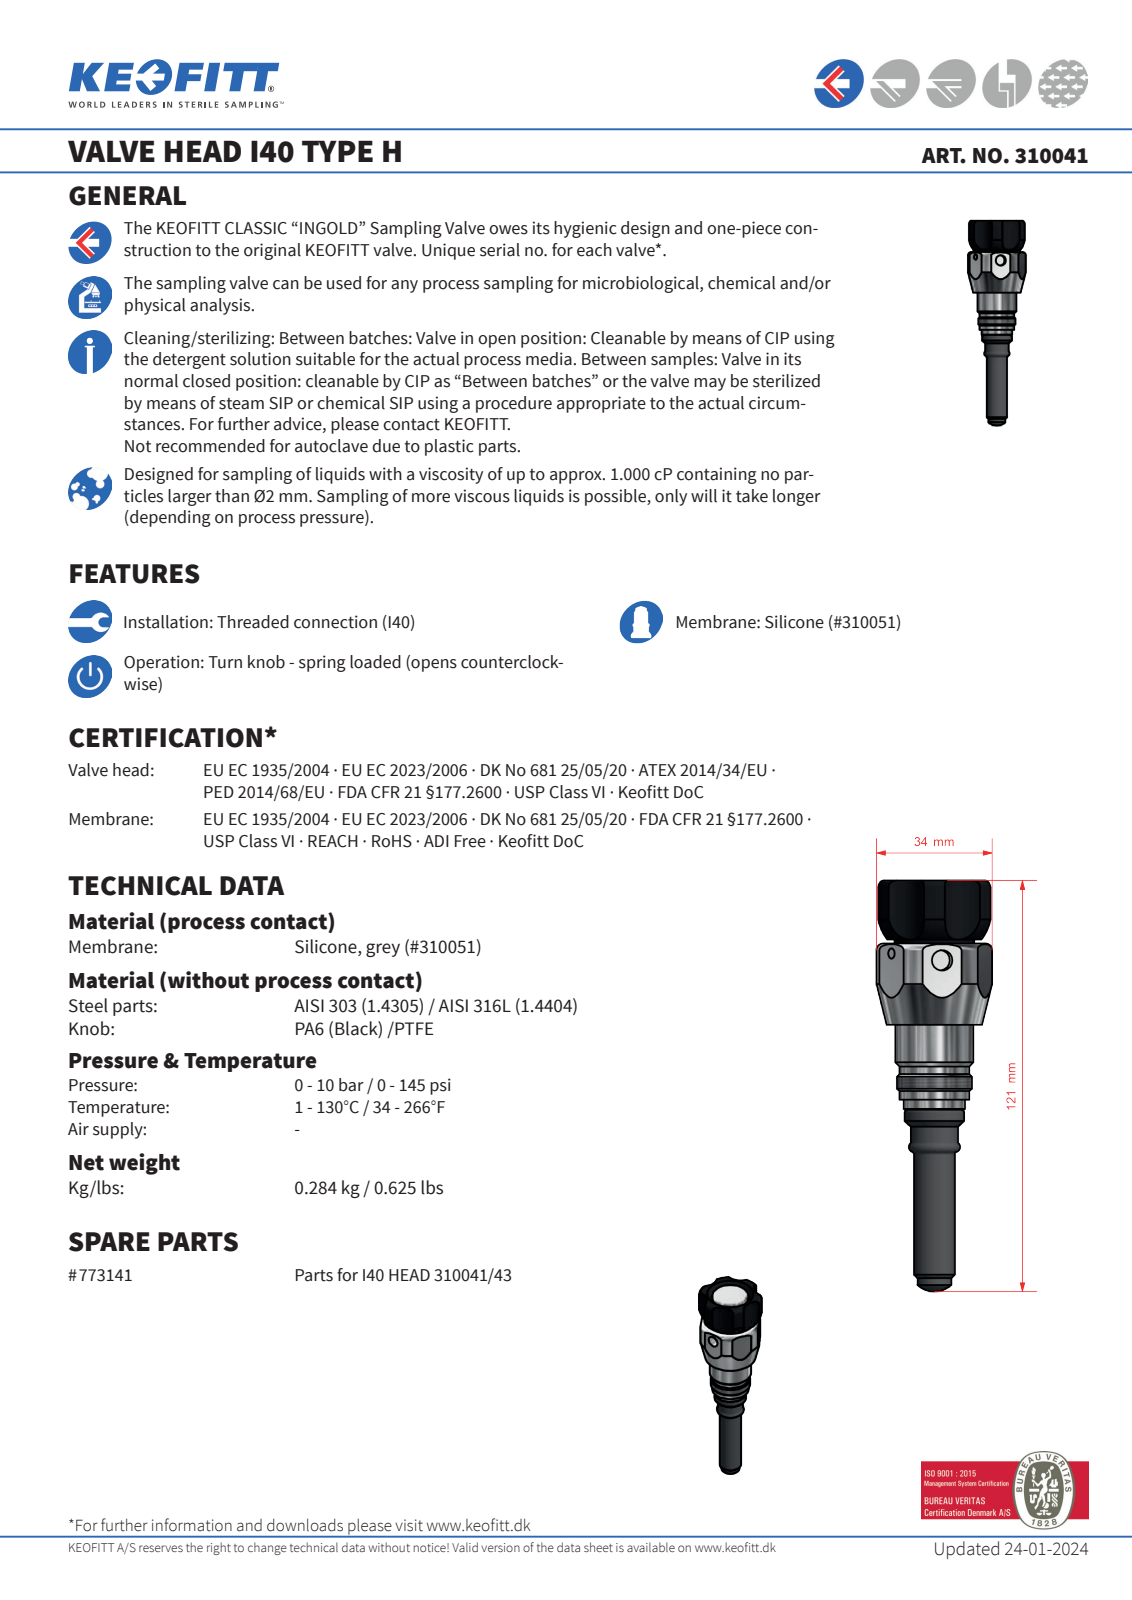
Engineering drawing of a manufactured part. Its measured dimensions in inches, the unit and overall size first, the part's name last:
Units: inches
Overall size (bounding box): 4.764 × 1.378 × 1.339
Round holes (diameter × count): ⌀0.238 ×2, ⌀0.12 ×1, ⌀0.402 ×1, ⌀0.583 ×1, ⌀0.669 ×1, ⌀0.713 ×1, ⌀0.732 ×1, ⌀0.762 ×1, ⌀0.811 ×1
Round bosses / shafts (diameter × count): ⌀0.925 ×1, ⌀0.906 ×1, ⌀0.866 ×1, ⌀0.807 ×1, ⌀0.787 ×1, ⌀0.709 ×1, ⌀0.689 ×1, ⌀0.61 ×1
Partial cylindrical surfaces — rounded edges, fillets, slot ends (radius × count): R0.315 ×6, R0.669 ×1, R0.689 ×1
Main face-to-face distances: 1.26, 0.709, 0.945, 1.654, 0.986, 0.041, 0.668, 1.673, 0.728, 0.687
Hole centre spacings: 0.079
Volume: 2.74 in³ · Surface area: 33.3 in²
Bodies: 1 solid, 127 faces (30 planar, 54 cylindrical, 43 other)
Part name (STEP PRODUCT): 310041
STEP written by: Autodesk Inventor 2017 (AUTOMOTIVE_DESIGN)
